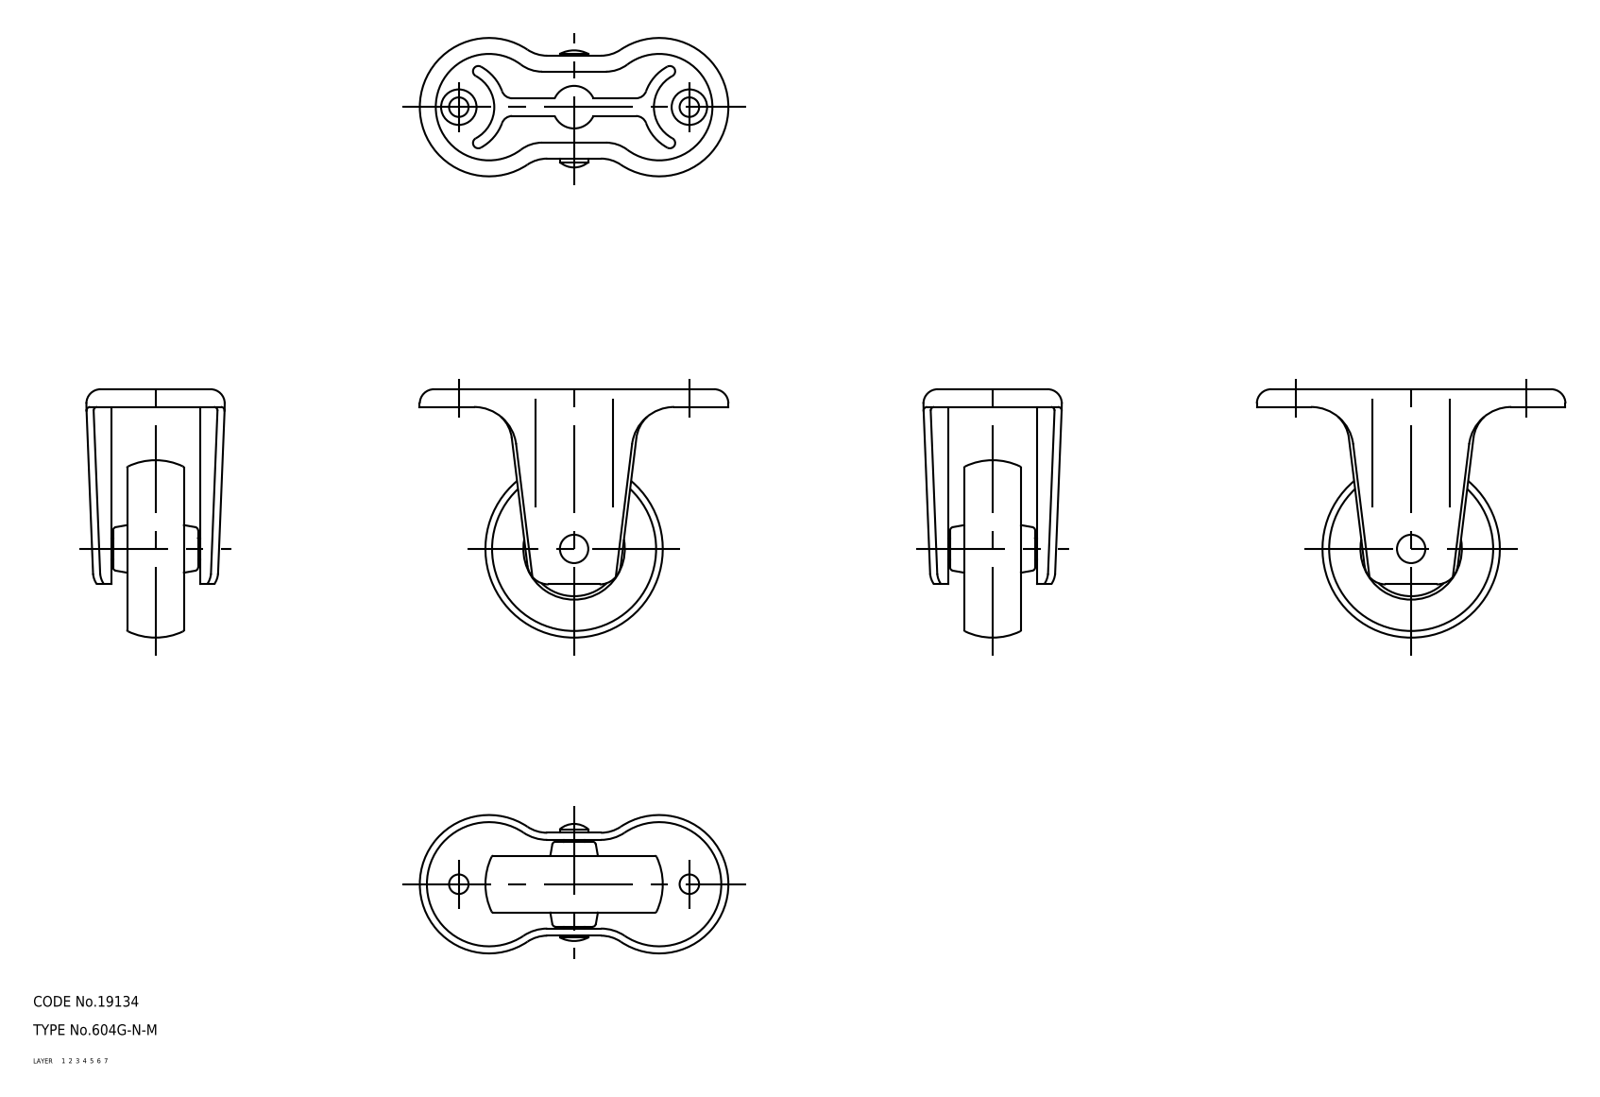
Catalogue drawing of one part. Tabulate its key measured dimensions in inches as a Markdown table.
| quantity | value |
| --- | --- |
| part name | wheel; axle; No_604G_N_M_14496_36 |
| STEP written by | CADfix (AUTOMOTIVE_DESIGN) |
| units | inches |
| bodies | 3 solids, 168 faces (0 planar, 0 cylindrical, 168 other) |
| overall size | 3.425 × 2.756 × 1.535 |
| volume | 2.414 in³ |
| surface area | 34.55 in² |
